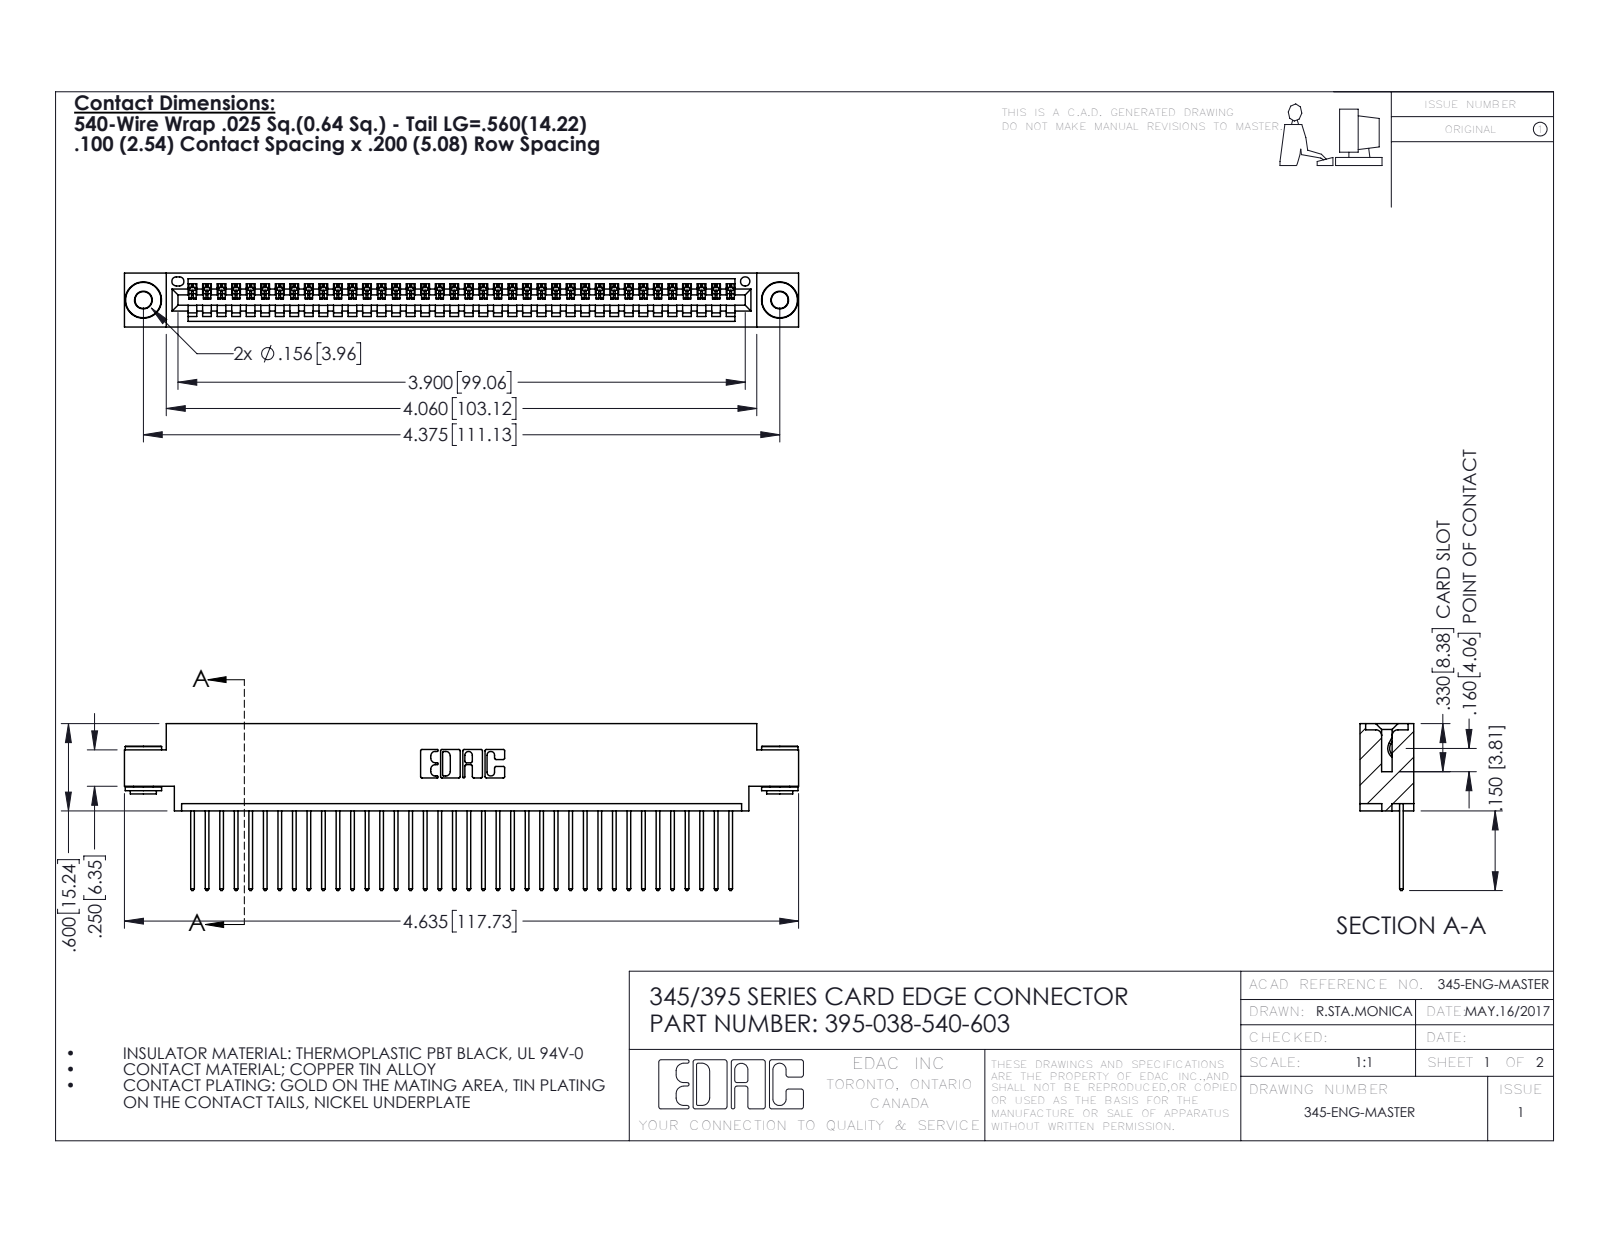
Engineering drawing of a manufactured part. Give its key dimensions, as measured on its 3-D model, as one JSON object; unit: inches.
{"part_name": "395-038-540-603; 345-292-001_345-293-140; 345-250-002_345-250-002-102; 345 Part_0.170 Offset - 0.156 Dia-TH", "step_written_by": "SolidWorks 2016 (CONFIG_CONTROL_DESIGN)", "units": "inches", "bodies": {"solids": 41, "faces": 2372, "planar": 1614, "cylindrical": 750, "other": 8}, "overall_size": [4.635, 1.147, 0.37], "volume_in3": 0.678, "surface_area_in2": 23.9, "round_holes": [[0.116, 2], [0.156, 2], [0.064, 1]], "round_bosses_or_shafts": [[0.25, 2], [0.18, 2], [0.136, 2]], "partial_cylinders_radius": [[0.006, 76], [0.01, 76], [0.01, 22], [0.007, 6], [0.031, 6], [0.026, 3], [0.031, 2], [0.04, 2]], "face_to_face_distances": [0.072, 0.298, 0.37, 0.098, 0.272, 0.025, 0.2, 0.225, 0.175, 0.149], "hole_center_spacings": [0.27, 4.139, 4.375]}
